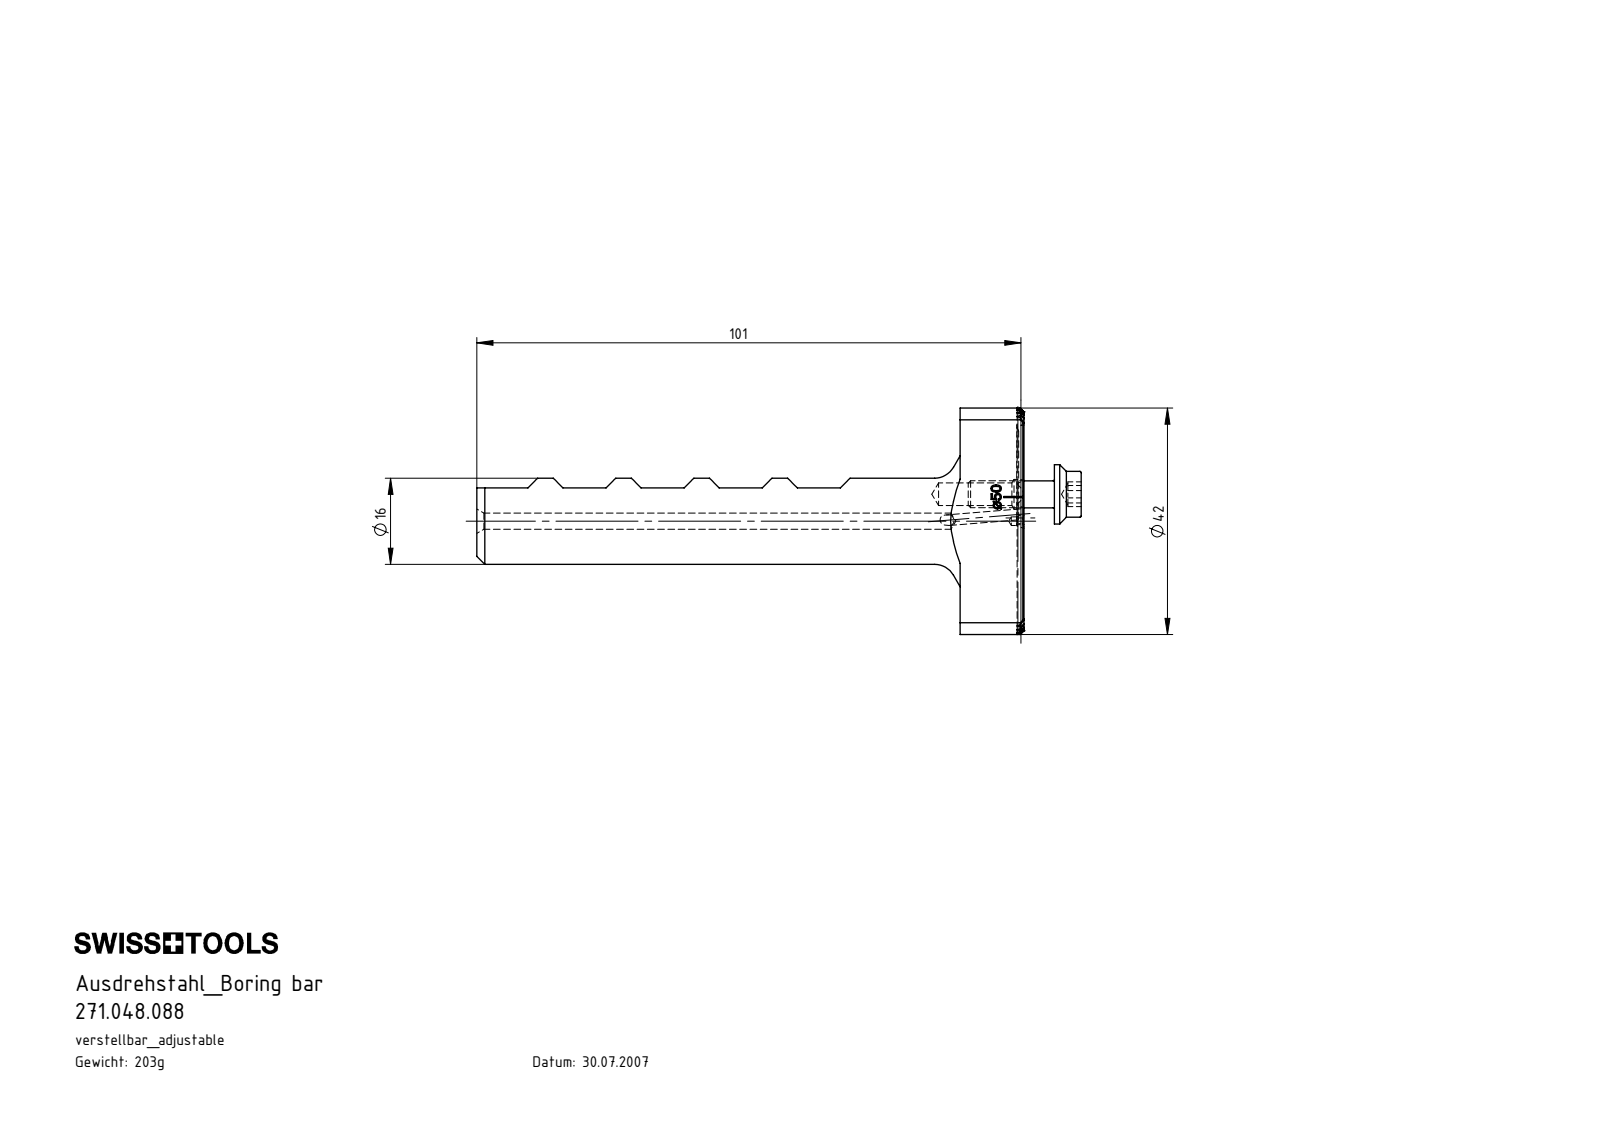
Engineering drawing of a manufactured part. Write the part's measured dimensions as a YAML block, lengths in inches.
part_name: "U16-BV2.K01.101"
step_written_by: "SolidWorks 2012 (CONFIG_CONTROL_DESIGN)"
units: inches
bodies: {solids: 1, faces: 190, planar: 91, cylindrical: 33, other: 66}
overall_size: [3.999, 1.654, 0.732]
volume: 1.543
surface_area: 13.69
round_holes:
  - {diameter: 0.063, count: 1}
  - {diameter: 0.079, count: 1}
  - {diameter: 0.118, count: 1}
  - {diameter: 0.165, count: 1}
  - {diameter: 0.217, count: 1}
round_bosses_or_shafts:
  - {diameter: 0.63, count: 1}
partial_cylinders:
  - {radius: 0.006, count: 9}
  - {radius: 0.049, count: 2}
  - {radius: 0.827, count: 1}
face_to_face_distances: [0.068, 0.732, 0.136, 0.341, 0.273, 0.205, 0.137, 0.204, 0.409, 0.069]
hole_center_spacings: [0.197]
